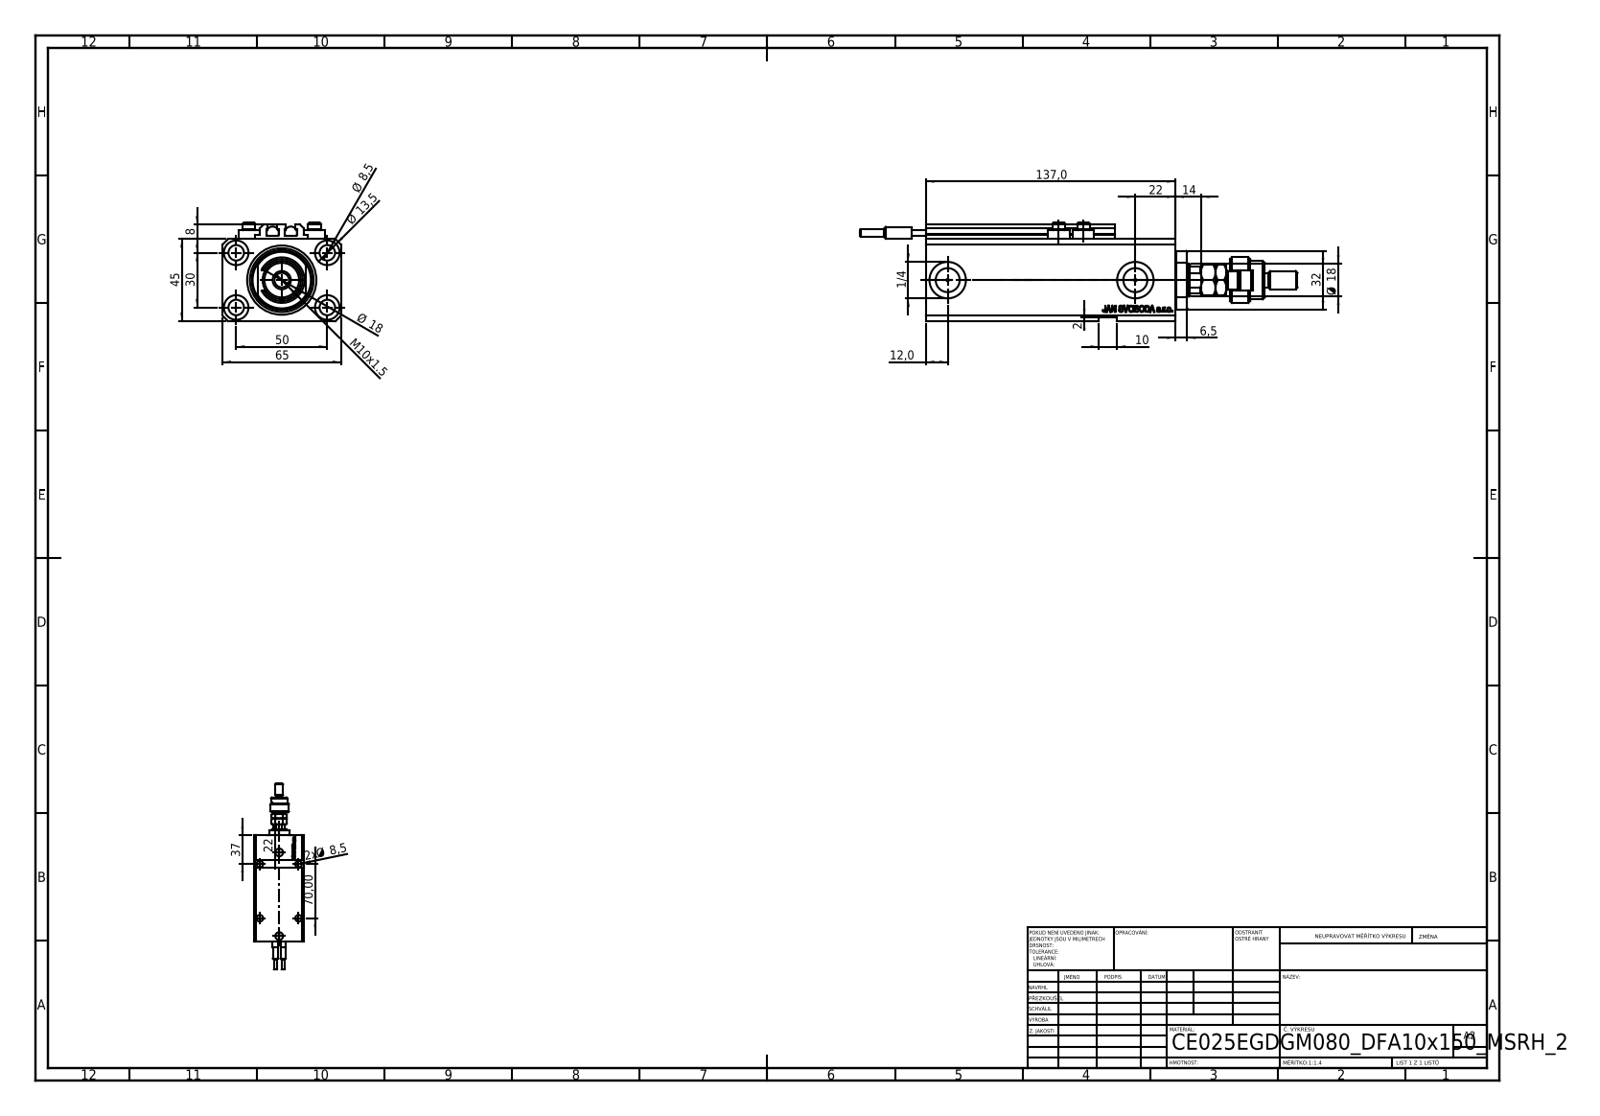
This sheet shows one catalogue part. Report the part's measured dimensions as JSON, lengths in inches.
{"part_name": "V250CE_VC_E; ALLEN BOLT V250CE; V250CE_C_VCP; FEMALE_PART_FOR_DFA (+3 more)", "step_written_by": "SolidWorks 2019 (CONFIG_CONTROL_DESIGN)", "units": "inches", "bodies": {"solids": 12, "faces": 1240, "planar": 575, "cylindrical": 183, "other": 482}, "overall_size": [9.449, 2.559, 2.126], "volume_in3": 22.11, "surface_area_in2": 159.5, "round_holes": [[0.335, 9], [0.049, 4], [0.157, 4], [0.531, 4], [0.394, 2], [0.518, 2], [0.787, 2], [0.709, 1], [1.496, 1]], "round_bosses_or_shafts": [[0.457, 4], [0.276, 4], [0.268, 2], [0.256, 2], [0.157, 2], [0.984, 1], [0.827, 1], [0.63, 1]], "partial_cylinders_radius": [[0.008, 10], [0.217, 1], [0.335, 1], [0.344, 1], [0.63, 1]], "face_to_face_distances": [1.772, 2.559, 0.551, 0.079, 1.85, 0.118, 0.098, 4.843, 0.394, 0.803], "hole_center_spacings": [1.148, 1.969, 0.535, 0.595, 1.098, 1.181, 1.323, 1.324]}
